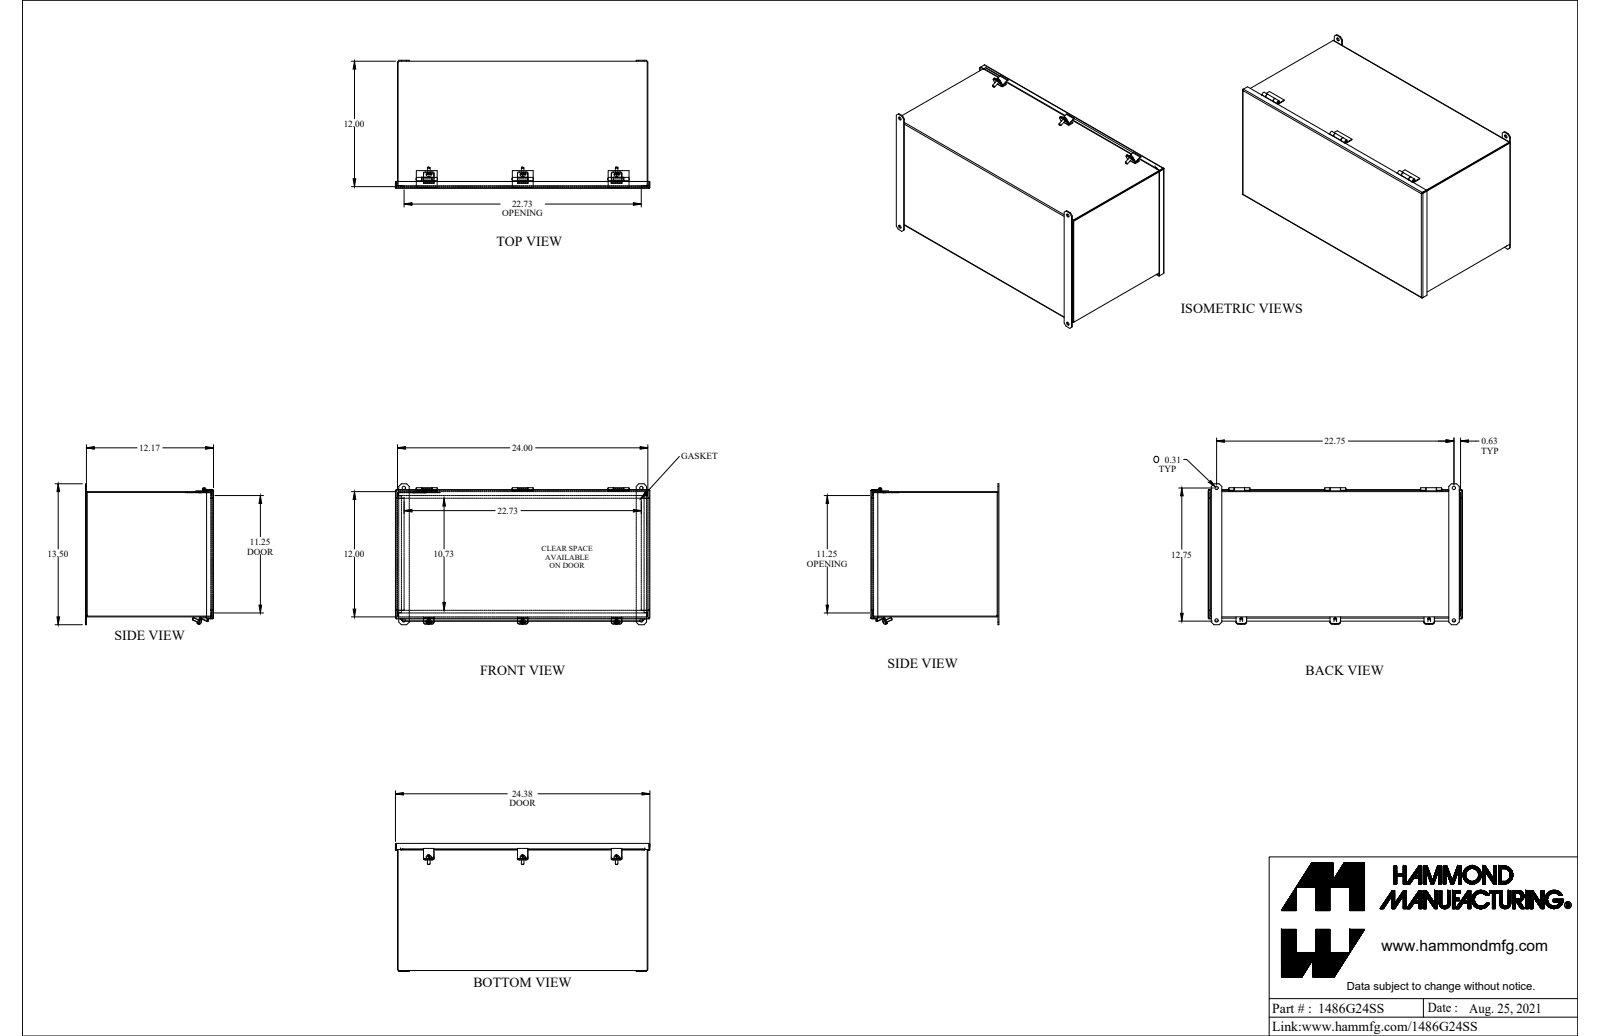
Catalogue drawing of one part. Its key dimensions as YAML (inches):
part_name: "1486G24"
step_written_by: "SolidWorks 2021 (AUTOMOTIVE_DESIGN)"
units: inches
bodies: {solids: 13, faces: 491, planar: 333, cylindrical: 129, other: 29}
overall_size: [24.375, 13.5, 12.267]
volume: 120.3
surface_area: 3202
round_holes:
  - {diameter: 0.313, count: 4}
  - {diameter: 0.213, count: 3}
  - {diameter: 0.187, count: 1}
round_bosses_or_shafts:
  - {diameter: 0.48, count: 3}
  - {diameter: 0.246, count: 3}
  - {diameter: 0.337, count: 1}
  - {diameter: 0.18, count: 1}
partial_cylinders:
  - {radius: 0.04, count: 8}
  - {radius: 0.11, count: 8}
  - {radius: 0.01, count: 6}
  - {radius: 0.03, count: 6}
  - {radius: 0.141, count: 6}
  - {radius: 0.188, count: 6}
  - {radius: 0.036, count: 5}
  - {radius: 0.108, count: 5}
face_to_face_distances: [0.07, 11.93, 0.072, 12, 11.86, 12.102, 12.03, 23.93, 12.172, 12.1]
hole_center_spacings: [9, 12.688, 22.75, 26.049, 18]
